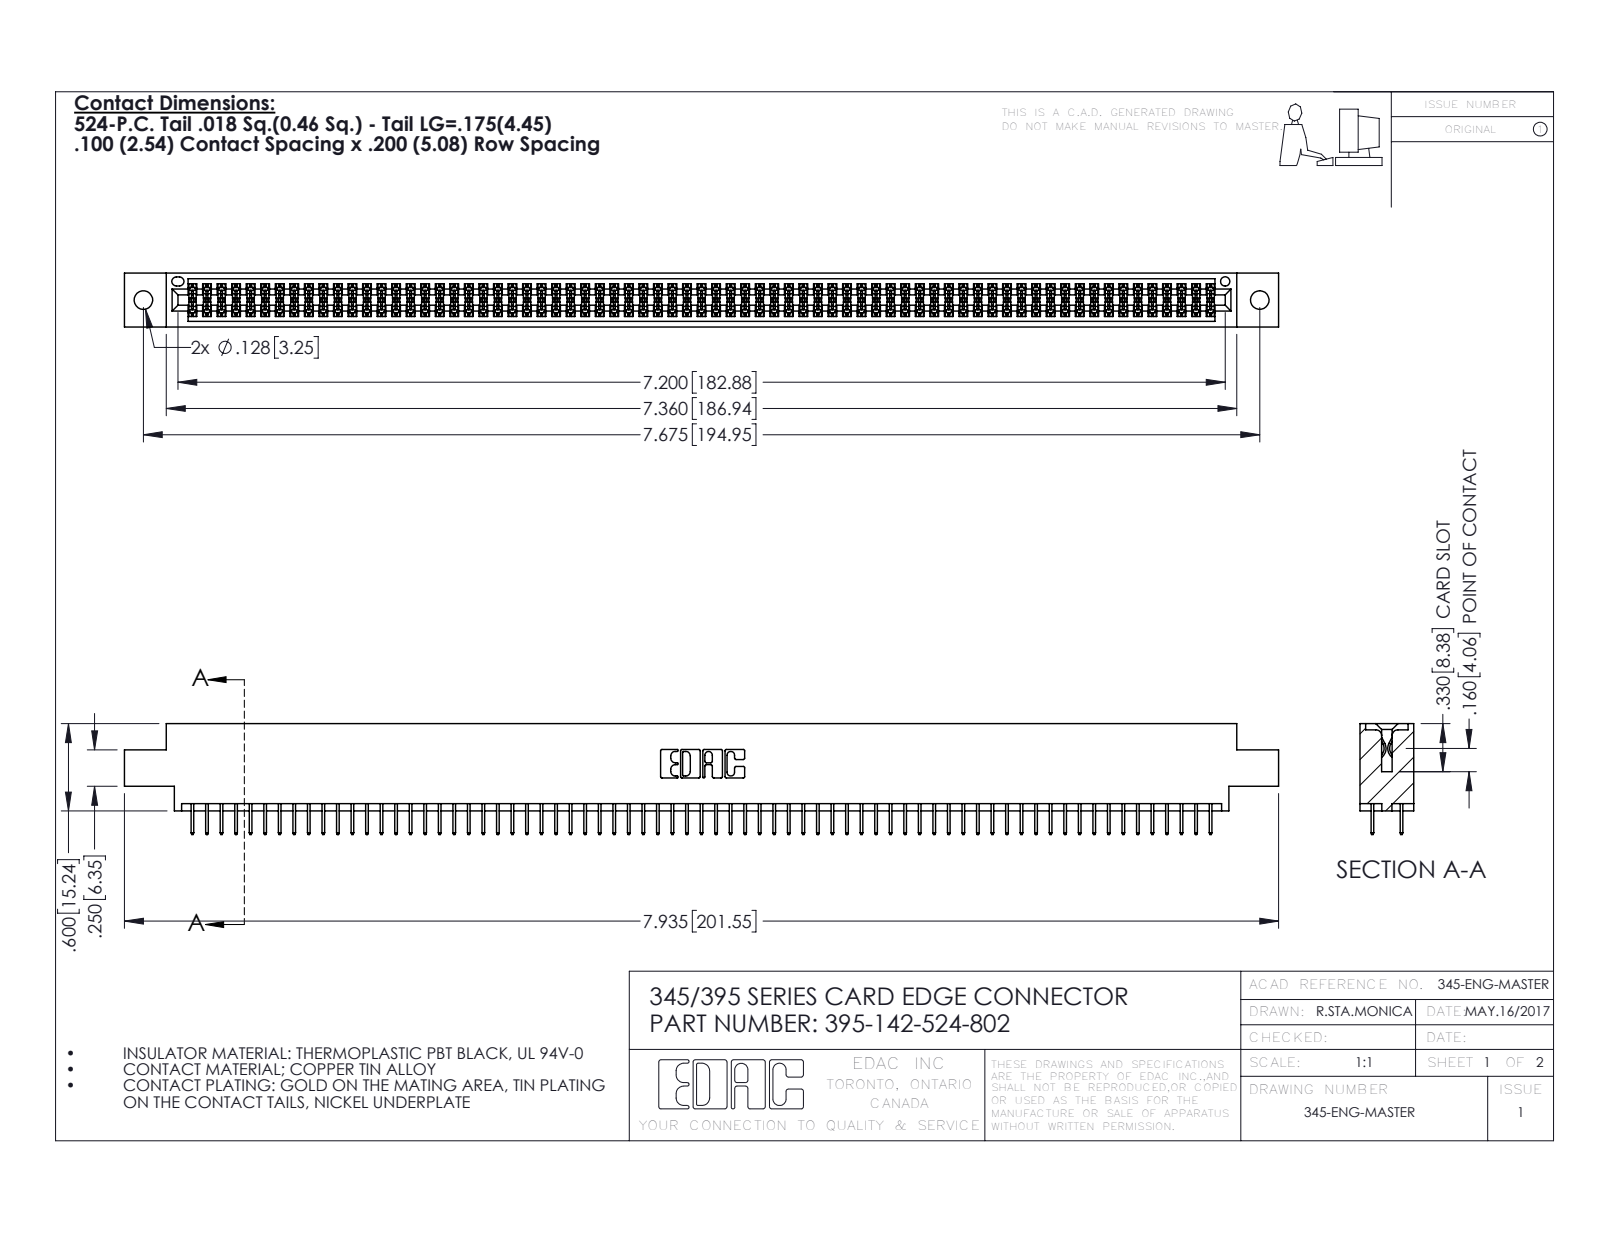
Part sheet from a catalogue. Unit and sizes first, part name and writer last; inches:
Units: inches
Overall size (bounding box): 7.935 × 0.762 × 0.37
Round holes (diameter × count): ⌀0.128 ×2, ⌀0.064 ×1
Partial cylindrical surfaces — rounded edges, fillets, slot ends (radius × count): R0.006 ×213, R0.01 ×22, R0.007 ×6, R0.031 ×6, R0.026 ×3, R0.014 ×2, R0.019 ×2, R0.022 ×2
Main face-to-face distances: 0.072, 0.298, 0.2, 0.37, 0.098, 0.272, 0.025, 0.225, 0.072, 0.175
Hole centre spacings: 0.27, 7.439, 7.675
Volume: 1.189 in³ · Surface area: 44.43 in²
Bodies: 143 solids, 7798 faces (5622 planar, 2176 cylindrical, 0 other)
Part name (STEP PRODUCT): 395-142-524-802; 345-292-001_345-293-124; 345 Part_0.170 Offset - 0.128 Dia
STEP written by: SolidWorks 2016 (CONFIG_CONTROL_DESIGN)
